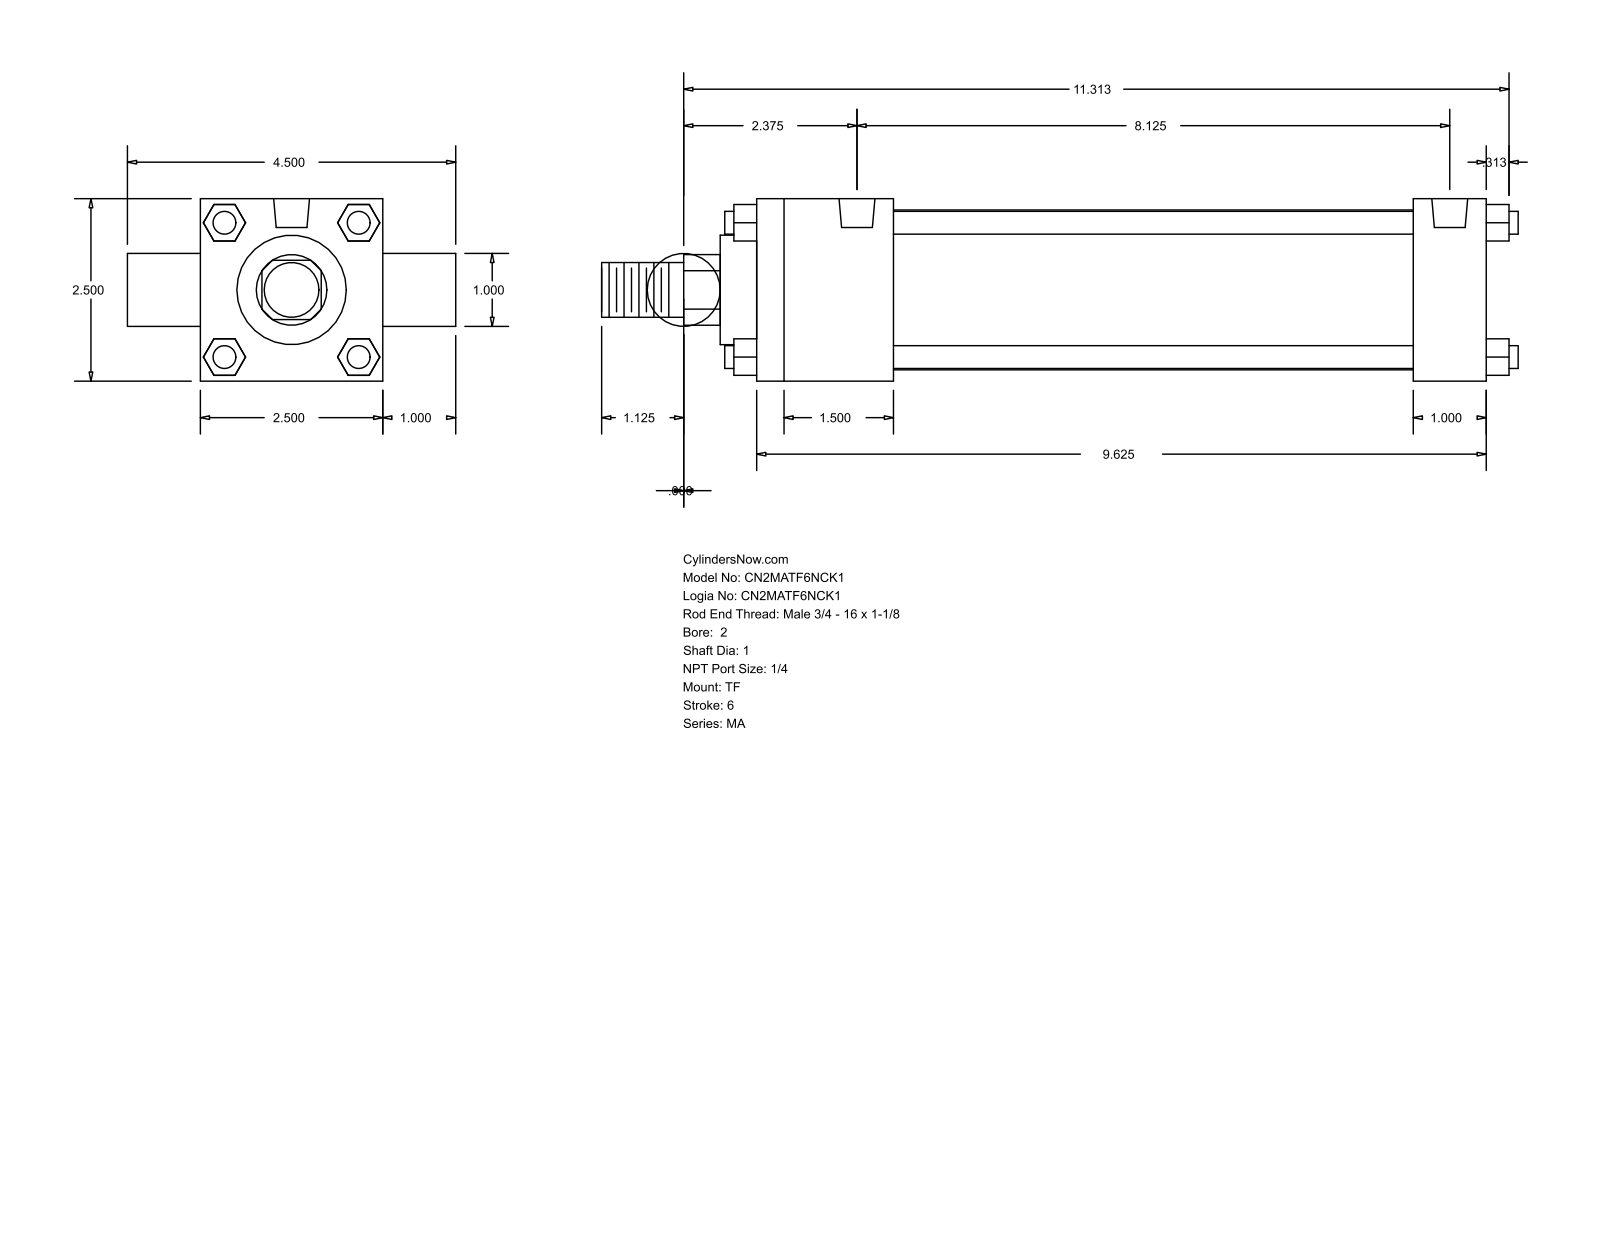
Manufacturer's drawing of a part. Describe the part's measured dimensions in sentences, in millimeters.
The part is named "MA_TF__0200_1". Its 3-D file was written by "GSSL Pune (CONFIG_CONTROL_DESIGN)". It is 0 solids with 120 faces: 92 planar, 28 cylindrical and 0 other. Overall it measures 319.09 by 114.3 by 63.5 millimeters. Round holes: 3 of diameter 7.94, 2 of diameter 12.49. Round bosses or shafts: 4 of diameter 7.94, 2 of diameter 25.4, 1 of diameter 55.63, 1 of diameter 38.1, 1 of diameter 19.05. Partial cylindrical surfaces (rounded edges, fillets, slot ends): 1 of radius 12.29. The main face-to-face distances are 63.5, 25.4, 254, 12.7, 47.63, 228.6, 180.97, 206.37, 88.9, 23.37. The hole center spacings are 206.37.
